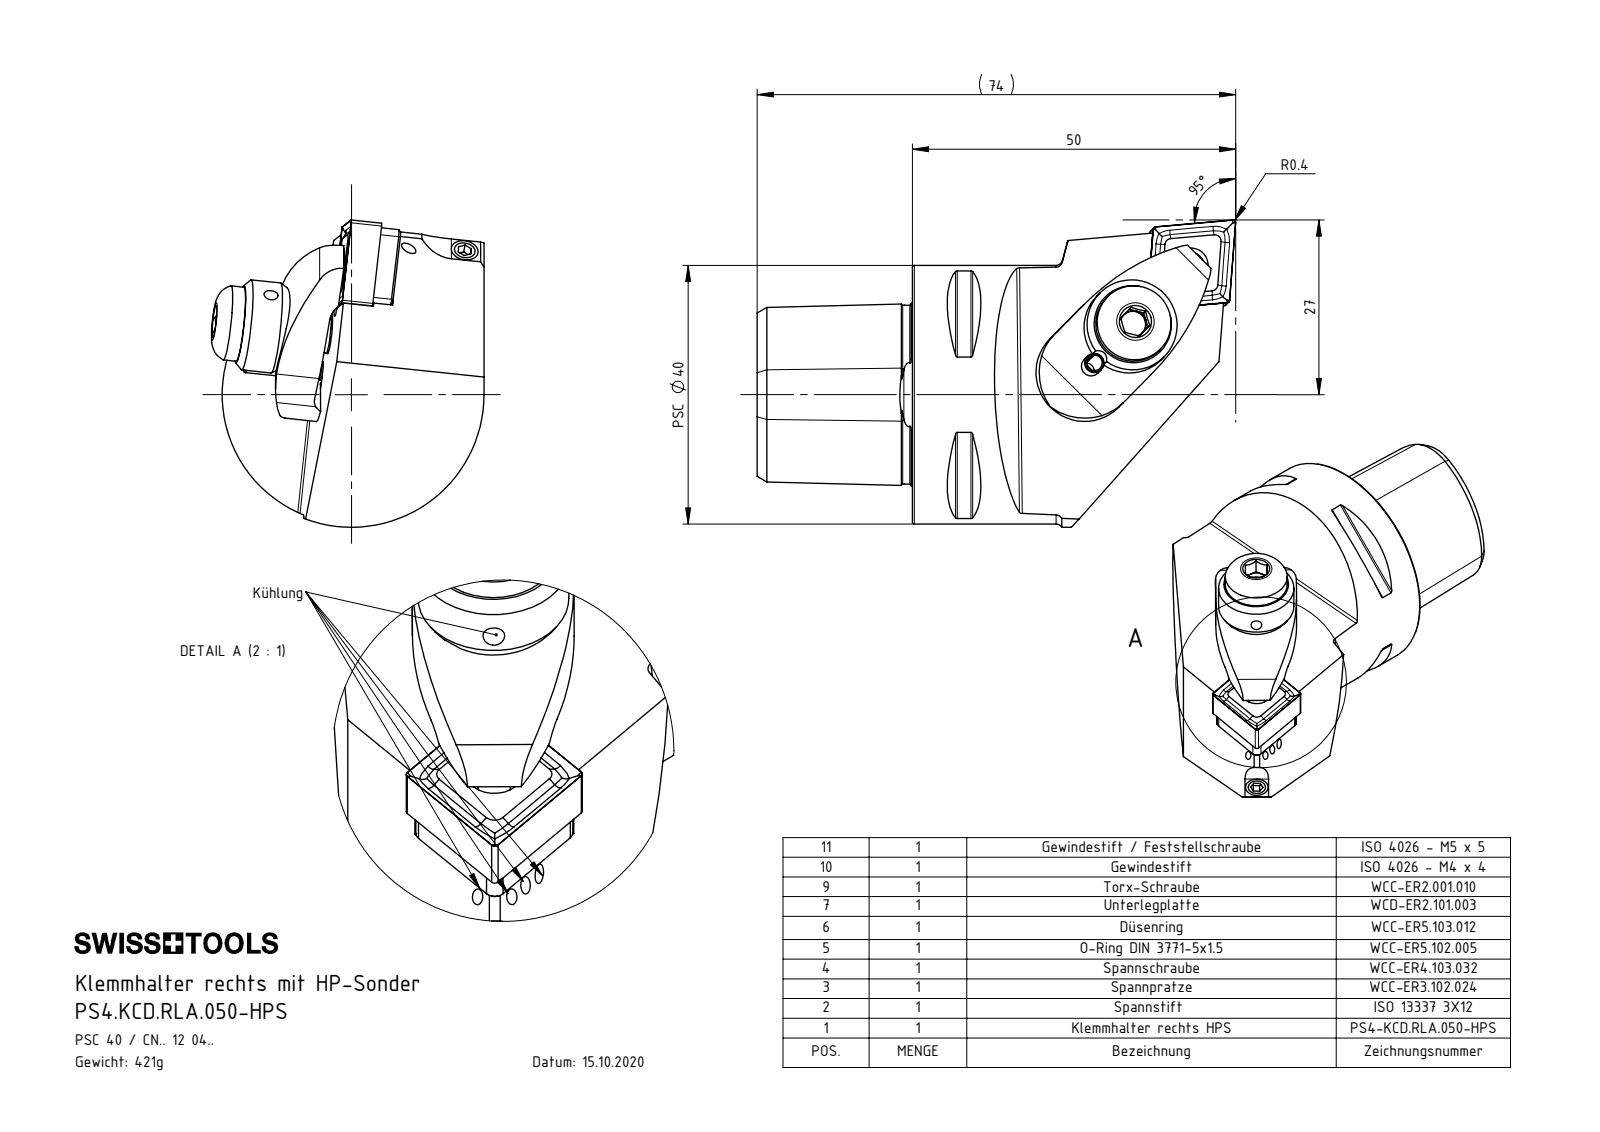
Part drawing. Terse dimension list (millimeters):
name: ISO 4026 - M4 x 4; WCC-ER4.103.032_B; CNMG120404; WCC-ER5.103.012_A (+8 more)
written by: SolidWorks 2022 (AUTOMOTIVE_DESIGN)
unit: mm
bodies: 11 solids, 333 faces (118 planar, 92 cylindrical, 123 other)
size: 74 × 47.5 × 42.16
volume: 52 630 mm³; area: 17 898 mm²
holes: 4× ⌀1.2, 3× ⌀2, 3× ⌀4.2, 2× ⌀5, 1× ⌀2.4, 1× ⌀3, 1× ⌀3.3, 1× ⌀4, 1× ⌀4.6, 1× ⌀5.16, 1× ⌀6.2, 1× ⌀6.55
bosses: 2× ⌀5, 2× ⌀4, 2× ⌀3, 1× ⌀40, 1× ⌀14, 1× ⌀11.5, 1× ⌀7, 1× ⌀6.8
rounds: 8× R0.3, 6× R0.39, 6× R0.69, 4× R0.4, 4× R1, 3× R3, 2× R2, 2× R40
face distances: 4.46, 1.3, 5.76, 24, 3.18, 7.64, 8.94, 0.5, 11.81, 15.52
hole spacings: 14.98, 23.3, 23.38, 6.78, 8.2, 8.21, 8.26, 8.32
